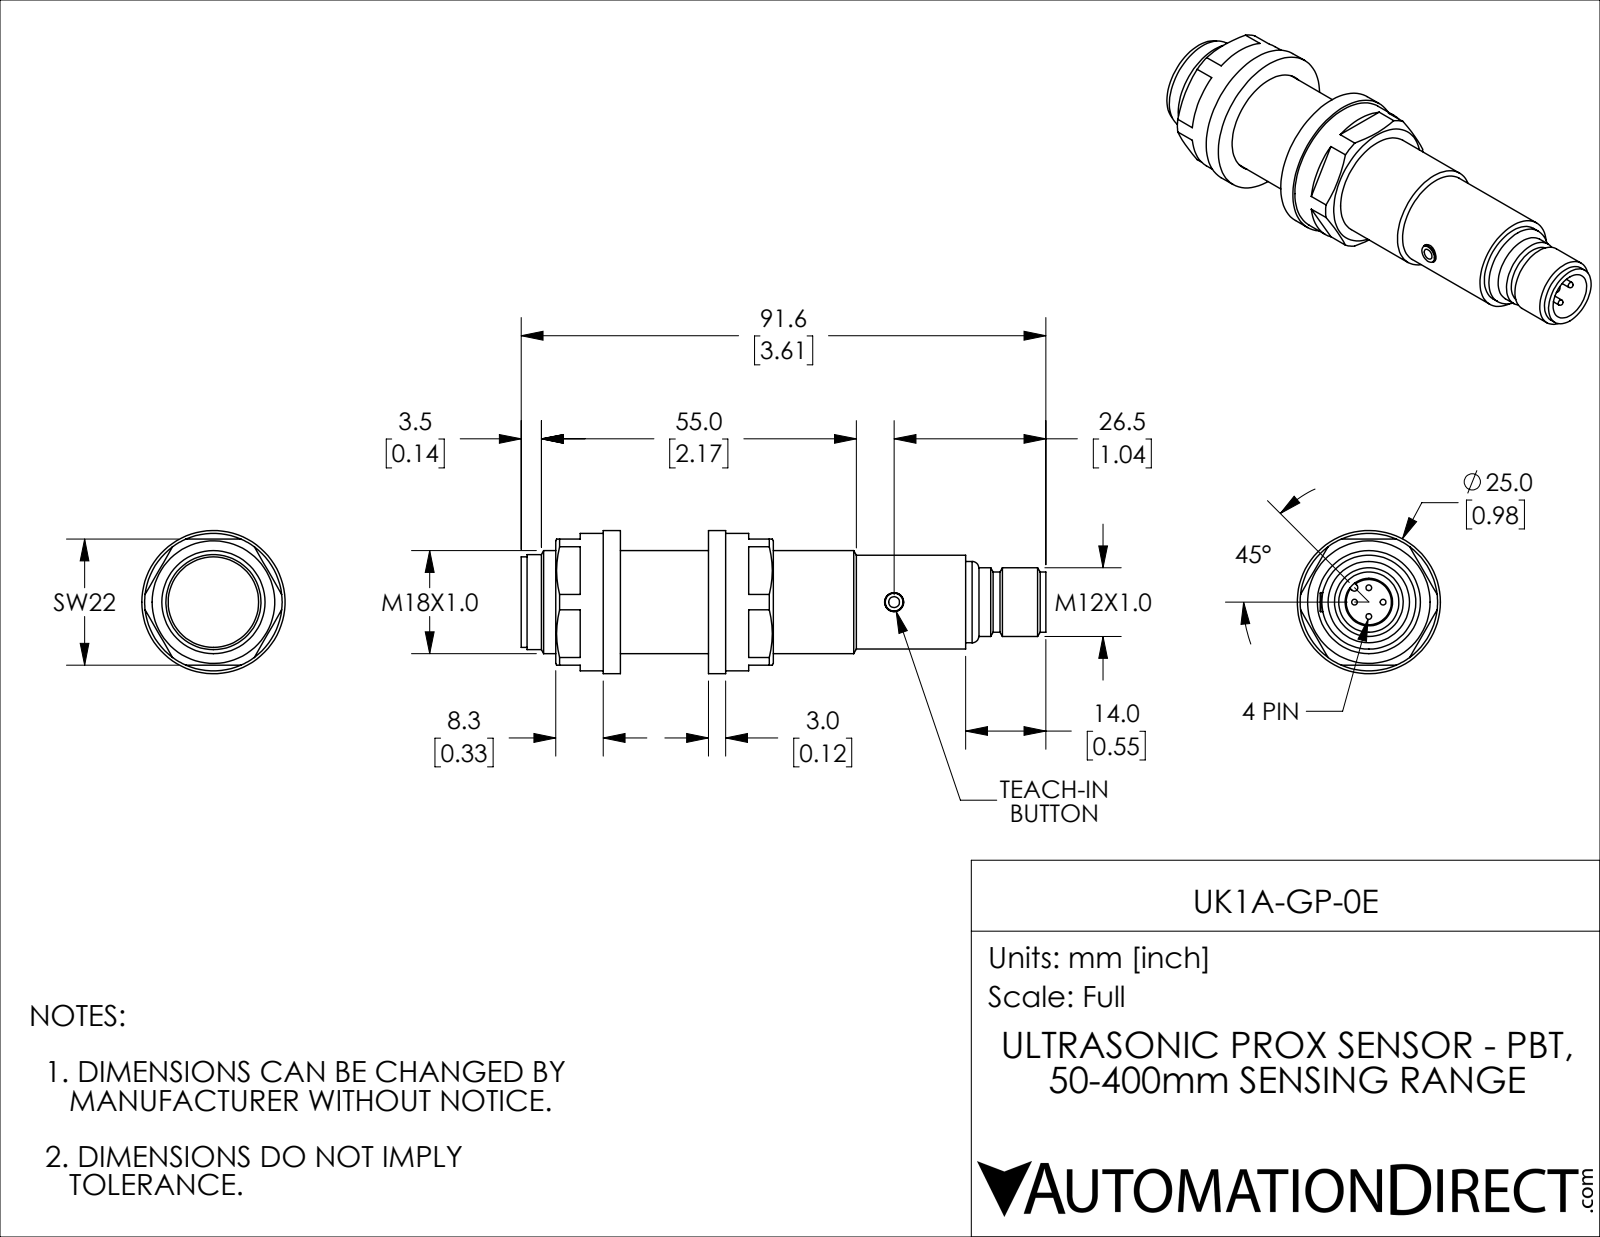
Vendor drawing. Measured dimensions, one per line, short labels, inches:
name: UK1A-GP-0E
written by: SolidWorks 2018 (AUTOMOTIVE_DESIGN)
unit: in
bodies: 6 solids, 123 faces (43 planar, 49 cylindrical, 31 other)
size: 3.606 × 0.984 × 0.984
volume: 1.477 in³; area: 16.01 in²
holes: 1× ⌀0.13, 1× ⌀0.327, 1× ⌀0.709, 1× ⌀0.717
bosses: 4× ⌀0.039, 1× ⌀0.984, 1× ⌀0.945, 1× ⌀0.654, 1× ⌀0.646, 1× ⌀0.622, 1× ⌀0.559, 1× ⌀0.472
rounds: 1× R0.024
face distances: 0.118, 0.724, 0.843, 0.606, 0.866, 0.327, 0.445, 1.051, 1.169, 0.563
